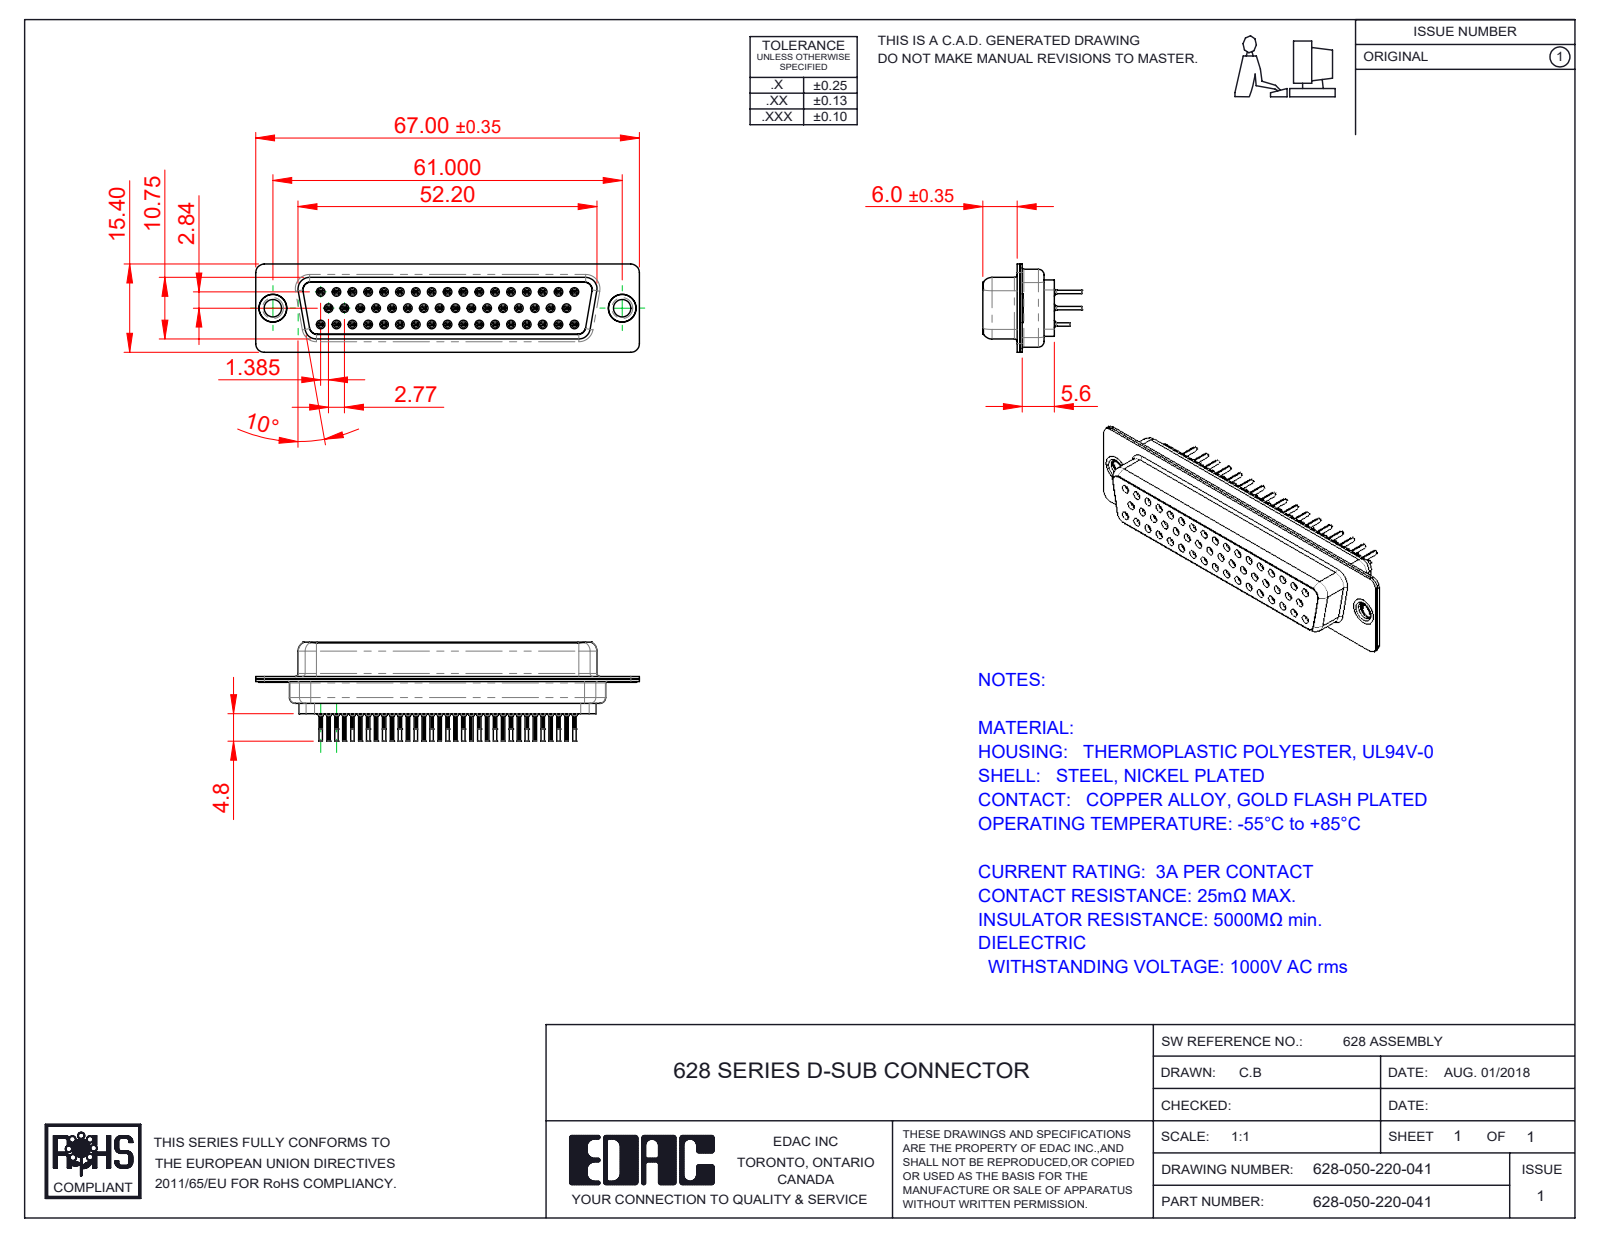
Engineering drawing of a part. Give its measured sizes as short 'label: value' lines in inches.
name: 628 Thru Hole Rivet; 628 Contact Row 3_20L; 628 Shell Rear_50 Contacts; 628 Housing_50 LP (+4 more)
written by: SolidWorks 2020 (CONFIG_CONTROL_DESIGN)
unit: in
bodies: 55 solids, 6603 faces (1617 planar, 1771 cylindrical, 3215 other)
size: 2.638 × 0.681 × 0.606
volume: 0.405 in³; area: 23.45 in²
holes: 50× ⌀0.008, 50× ⌀0.031, 50× ⌀0.035, 50× ⌀0.043, 50× ⌀0.063, 17× ⌀0.067, 2× ⌀0.12, 2× ⌀0.157, 2× ⌀0.159, 2× ⌀0.191
bosses: 50× ⌀0.079, 50× ⌀0.059, 50× ⌀0.047, 50× ⌀0.024, 2× ⌀0.197, 2× ⌀0.195, 2× ⌀0.189, 2× ⌀0.14
rounds: 100× R0.004, 33× R0.011, 16× R0.059, 12× R0.079, 8× R0.053, 4× R0.01, 4× R0.02, 4× R0.024
face distances: 0.018, 0.016, 0.446, 0.074, 0.238, 0.406, 0.035, 0.256, 0.071, 0.254
hole spacings: 0.124, 0.109, 0.218, 0.327, 0.436, 0.545, 0.654, 0.763
